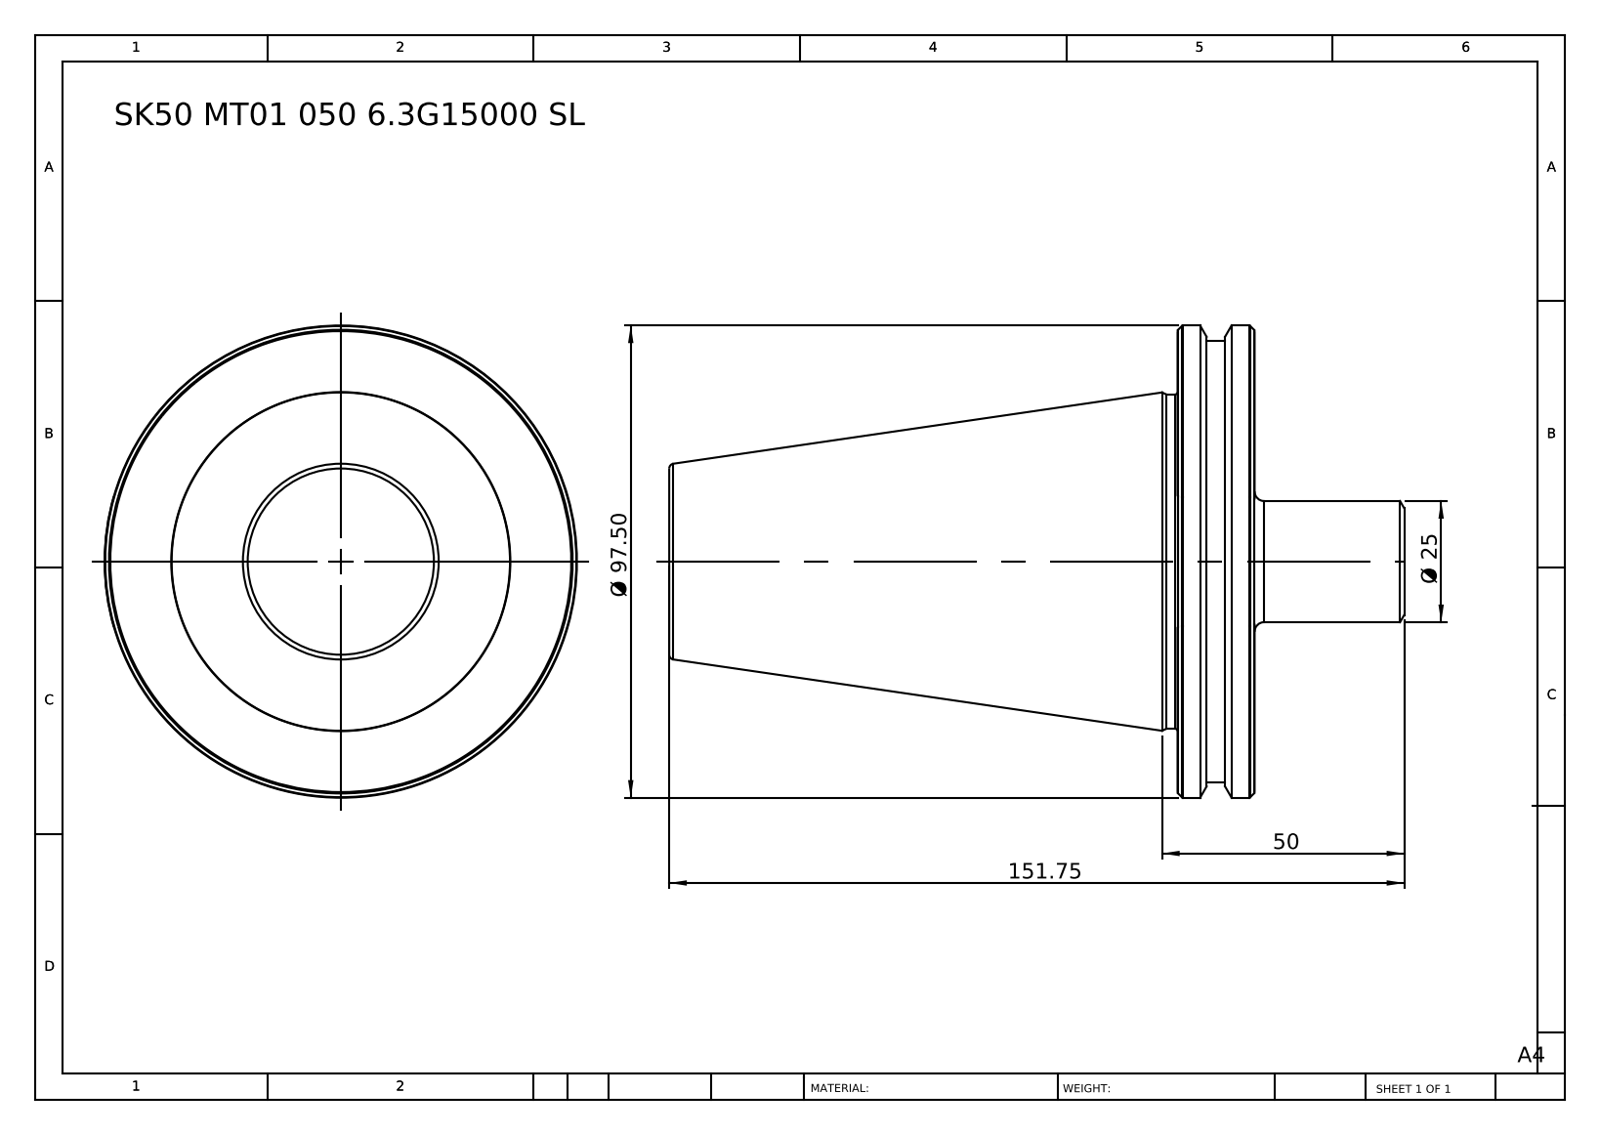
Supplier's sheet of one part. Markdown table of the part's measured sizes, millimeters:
| quantity | value |
| --- | --- |
| part name | SK 50 MT01 050 6.3G15000 SL |
| STEP written by | SolidWorks 2014 (CONFIG_CONTROL_DESIGN) |
| units | millimeters |
| bodies | 1 solid, 60 faces (6 planar, 10 cylindrical, 44 other) |
| overall size | 151.75 × 97.5 × 97.5 |
| volume | 388 695 mm³ |
| surface area | 38 896 mm² |
| round bosses / shafts (diameter × count) | 97.5 × 1, 91 × 1, 69 × 1, 25 × 1 |
| main face-to-face distances | 15.9, 120.85, 104.95, 30.9, 46.8, 151.75, 37, 6.1, 9.8, 114.75 |
